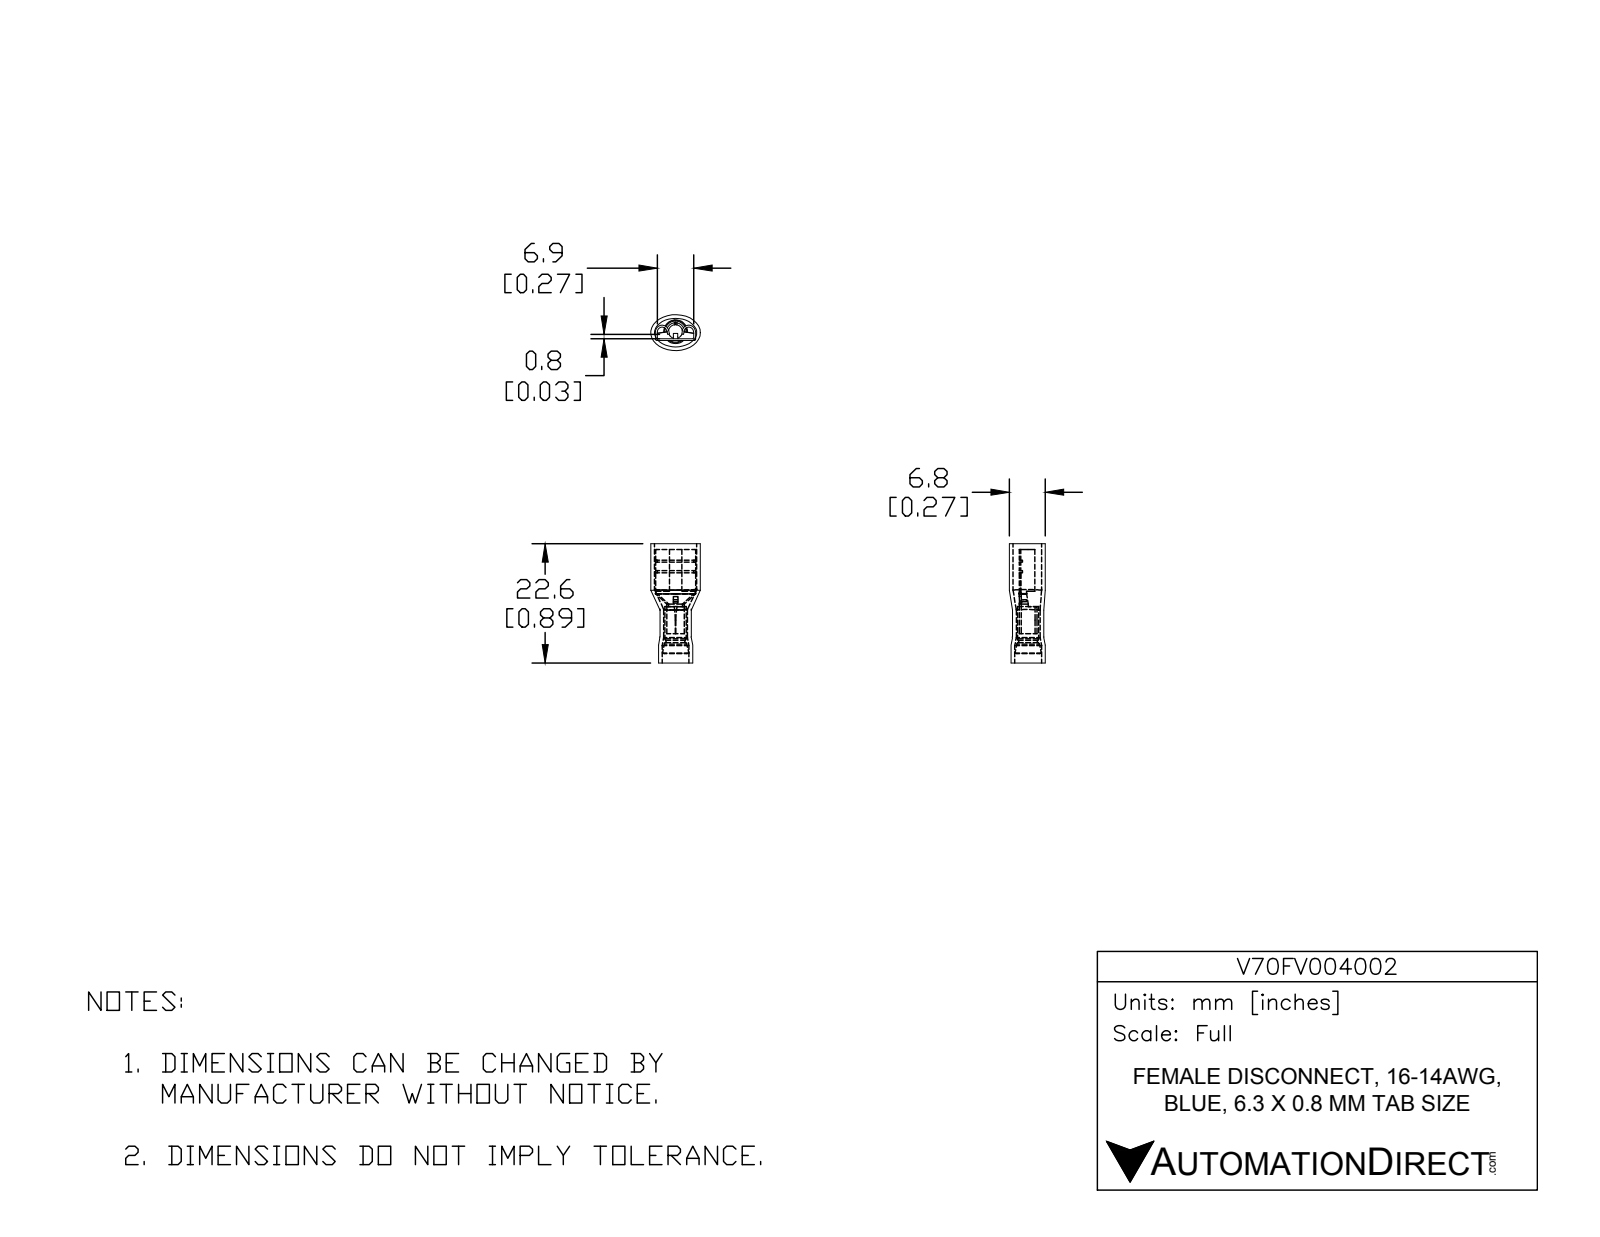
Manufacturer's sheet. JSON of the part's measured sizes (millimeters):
{"part_name": "V70FV004002", "step_written_by": "SolidWorks 2017 (AUTOMOTIVE_DESIGN)", "units": "millimeters", "bodies": {"solids": 3, "faces": 127, "planar": 51, "cylindrical": 36, "other": 40}, "overall_size": [22.58, 9.39, 6.8], "volume_mm3": 426, "surface_area_mm2": 1611, "round_holes": [[2.63, 1], [3.32, 1], [4.51, 1], [5.07, 1]], "round_bosses_or_shafts": [[6.47, 1], [5.91, 1], [4.02, 1], [3.33, 1]], "partial_cylinders_radius": [[0.12, 2], [0.25, 2], [0.91, 2], [1.26, 2], [16.36, 2], [0.37, 1], [0.72, 1]], "face_to_face_distances": [0.35, 7.23, 22.58, 7.58, 6.88, 2, 21.48, 1.1, 0.4, 2.4]}
